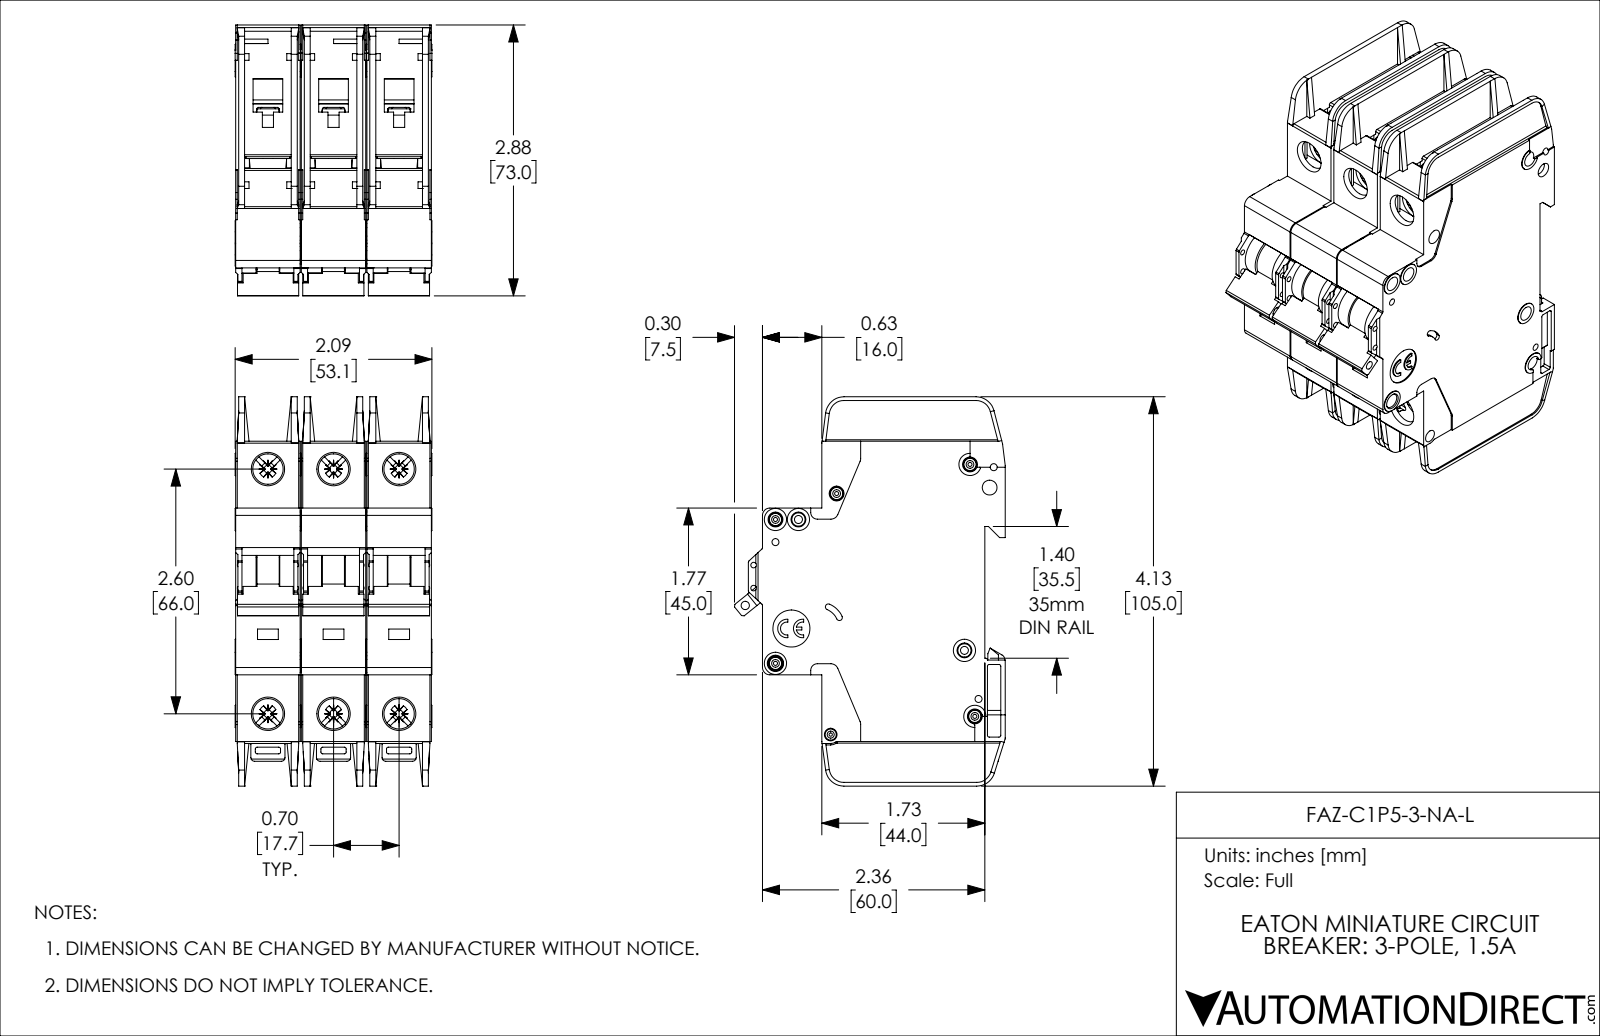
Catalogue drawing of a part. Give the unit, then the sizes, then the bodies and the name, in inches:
Units: inches
Overall size (bounding box): 4.134 × 2.876 × 2.091
Round holes (diameter × count): ⌀0.157 ×8, ⌀0.323 ×6, ⌀0.043 ×5, ⌀0.075 ×4, ⌀0.059 ×2, ⌀0.085 ×2, ⌀0.035 ×1, ⌀0.089 ×1, ⌀0.098 ×1, ⌀0.134 ×1, ⌀0.394 ×1
Round bosses / shafts (diameter × count): ⌀0.13 ×5, ⌀0.236 ×4, ⌀0.118 ×4, ⌀0.098 ×3
Partial cylindrical surfaces — rounded edges, fillets, slot ends (radius × count): R0.02 ×72, R0.016 ×30, R0.039 ×18, R0.043 ×12, R0.079 ×12, R0.008 ×6, R0.01 ×6, R0.028 ×6
Main face-to-face distances: 0.697, 0.047, 1.394, 0.685, 0.591, 1.382, 0.744, 0.65, 0.106, 0.094
Hole centre spacings: 0.697, 2.69, 2.598, 0.244, 0.537, 0.87, 1.394, 2.948
Volume: 14.05 in³ · Surface area: 123 in²
Bodies: 3 solids, 3381 faces (2013 planar, 1071 cylindrical, 297 other)
Part name (STEP PRODUCT): FAZ-C1P5-3-NA-L
STEP written by: SolidWorks 2019 (AUTOMOTIVE_DESIGN)
